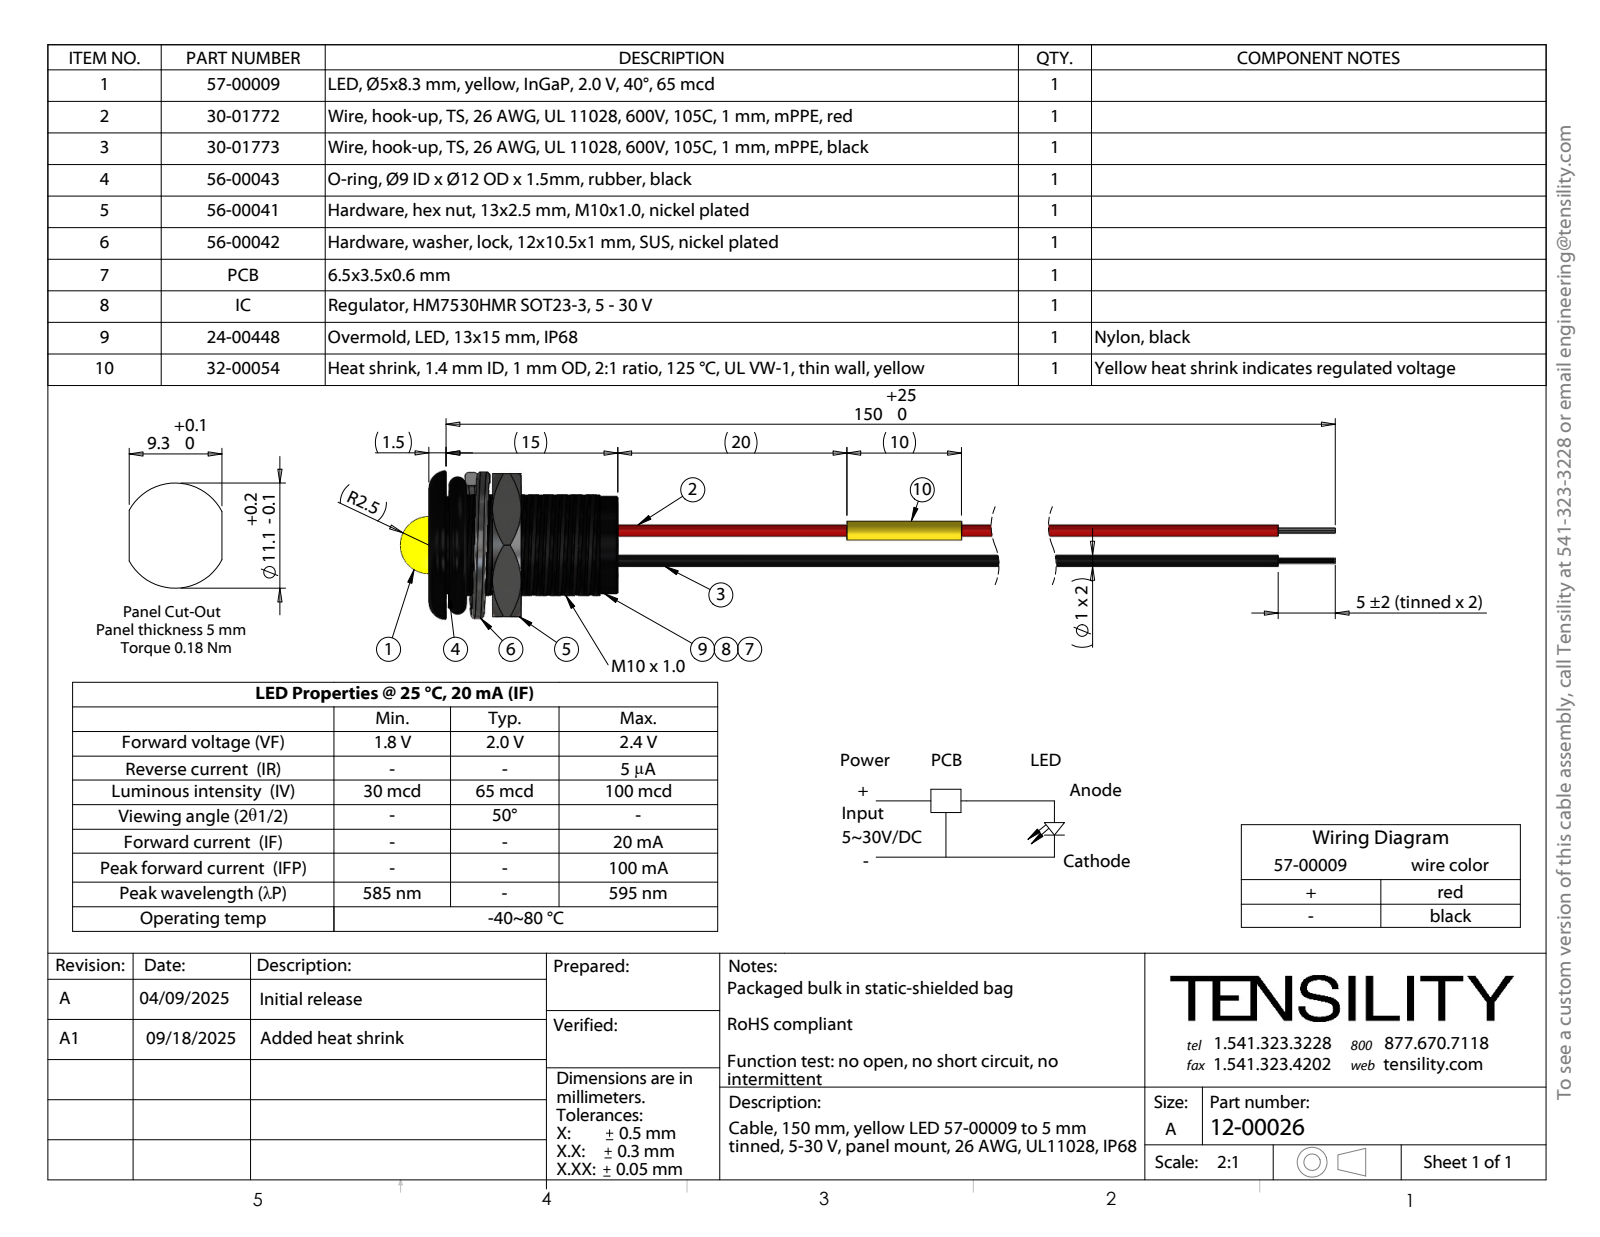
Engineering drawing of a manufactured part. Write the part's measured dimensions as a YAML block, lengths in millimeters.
part_name: "30-01773_stripped and tinned; 56-00043; 56-00041; 56-00042_Split washer (+4 more)"
step_written_by: "SolidWorks 2021 (CONFIG_CONTROL_DESIGN)"
units: millimeters
bodies: {solids: 57, faces: 514, planar: 185, cylindrical: 246, other: 83}
overall_size: [173.99, 14.43, 12.99]
volume: 1769
surface_area: 6568
round_holes:
  - {diameter: 1, count: 2}
round_bosses_or_shafts:
  - {diameter: 1, count: 2}
  - {diameter: 0.83, count: 2}
  - {diameter: 8.5, count: 1}
  - {diameter: 5, count: 1}
partial_cylinders:
  - {radius: 4.33, count: 1}
  - {radius: 5, count: 1}
face_to_face_distances: [1.5, 16.5, 15, 12.5, 8.06, 6.56, 8.44, 5.56, 4.06, 2.5]
hole_center_spacings: [0.36, 0.38, 0.33, 2.43, 2.35, 2.48, 2.52, 2.56]
